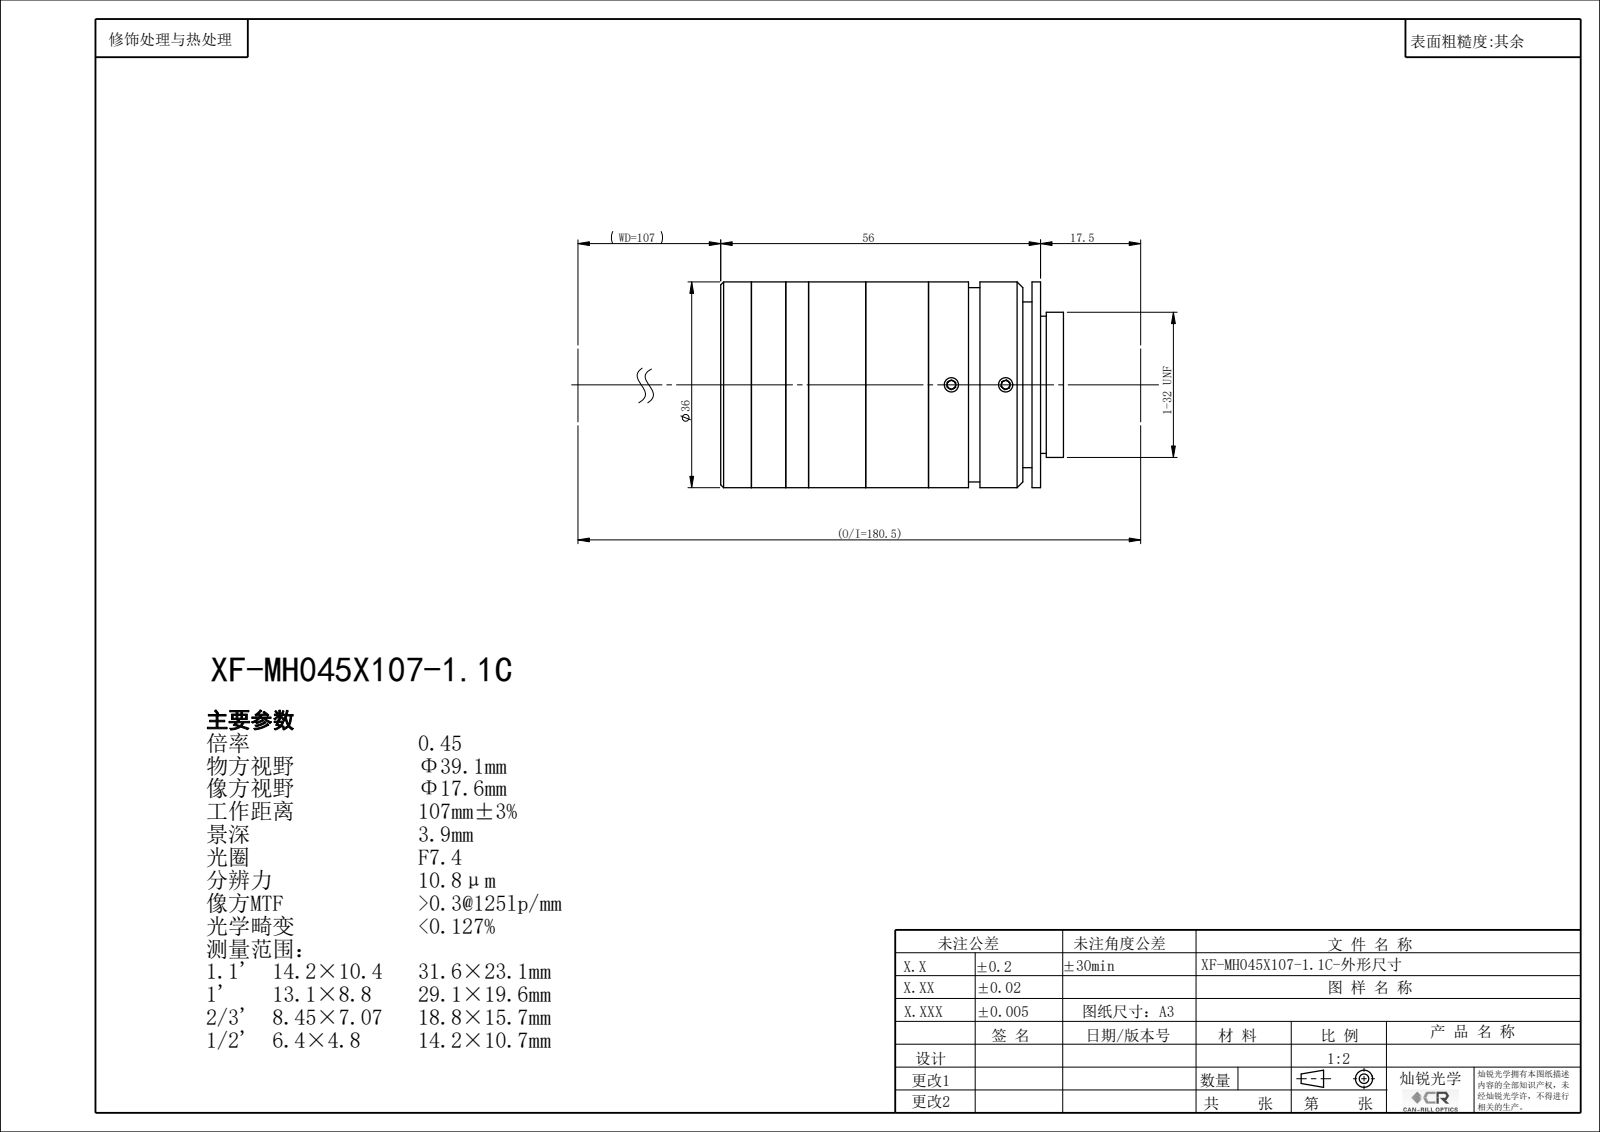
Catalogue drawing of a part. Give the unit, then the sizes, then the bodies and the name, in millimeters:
Units: millimetres
Overall size (bounding box): 59.99 × 36 × 36
Round holes (diameter × count): ⌀2.5 ×6, ⌀15 ×1, ⌀17.4 ×1, ⌀22.4 ×1, ⌀24 ×1, ⌀24.9 ×1, ⌀26 ×1, ⌀26.4 ×1
Round bosses / shafts (diameter × count): ⌀36 ×1, ⌀34 ×1, ⌀25.4 ×1
Main face-to-face distances: 19.61, 36.38, 55.99, 1.5, 54.49, 18.11, 10, 25.38, 11, 29.11
Hole centre spacings: 9.5
Bodies: 0 solids, 142 faces (74 planar, 48 cylindrical, 20 other)
Part name (STEP PRODUCT): XF-MH045X107-1.1C
STEP written by: SolidWorks 2022 (CONFIG_CONTROL_DESIGN)
